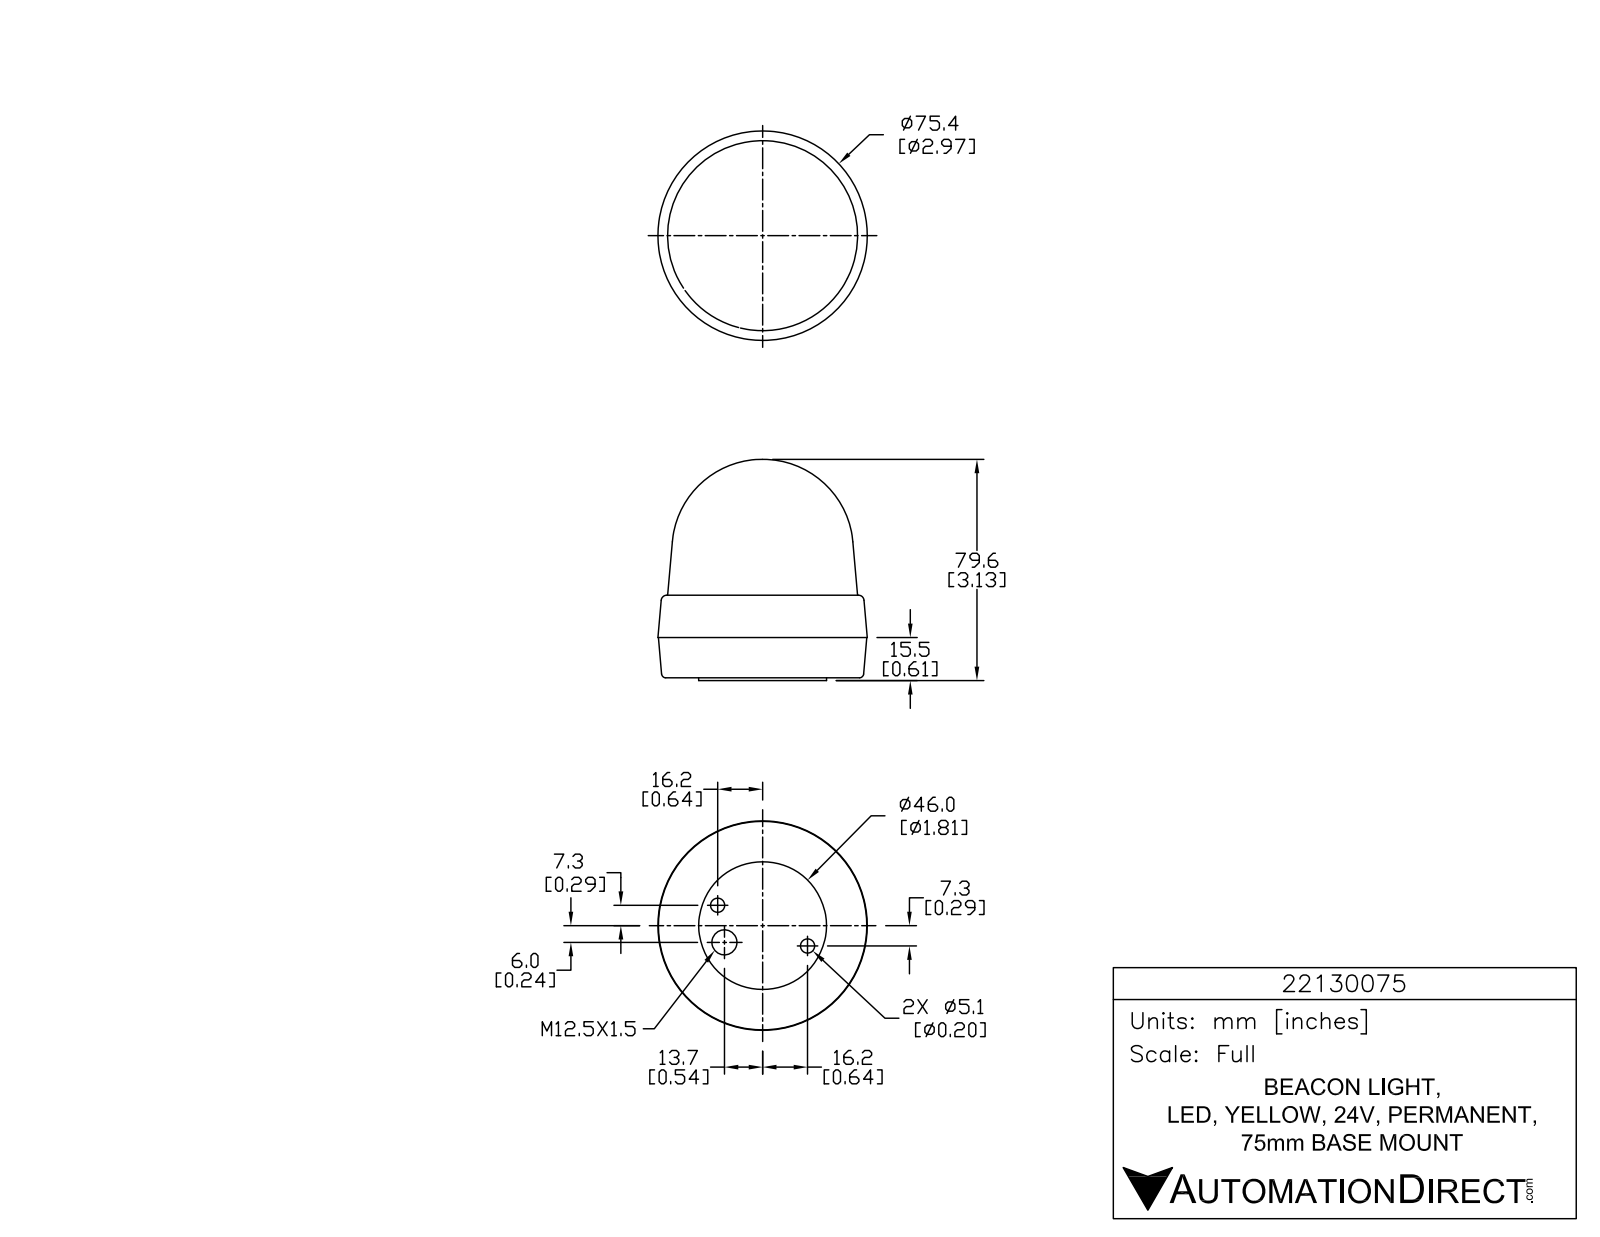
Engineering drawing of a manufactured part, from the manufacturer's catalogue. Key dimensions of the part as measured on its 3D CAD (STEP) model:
Part name (STEP PRODUCT): 22130075
STEP written by: SolidWorks 2015 (AUTOMOTIVE_DESIGN)
Units: inches
Bodies: 1 solid, 773 faces (526 planar, 163 cylindrical, 84 other)
Overall size (bounding box): 3.133 × 2.967 × 2.967
Volume: 15.79 in³ · Surface area: 33.7 in²
Round holes (diameter × count): ⌀0.059 ×3, ⌀0.201 ×2, ⌀0.354 ×1
Round bosses / shafts (diameter × count): ⌀0.339 ×3, ⌀0.084 ×3, ⌀1.811 ×1
Partial cylindrical surfaces — rounded edges, fillets, slot ends (radius × count): R0.005 ×9, R0.005 ×6, R0.012 ×6, R0.012 ×6, R0.012 ×6, R0.196 ×6, R0.005 ×3, R0.005 ×3
Main face-to-face distances: 0.039, 1.209, 1.17, 0.61, 0.571, 0.599, 1.566, 1.527, 0.956, 0.357
Hole centre spacings: 0.534, 1.179, 1.398
